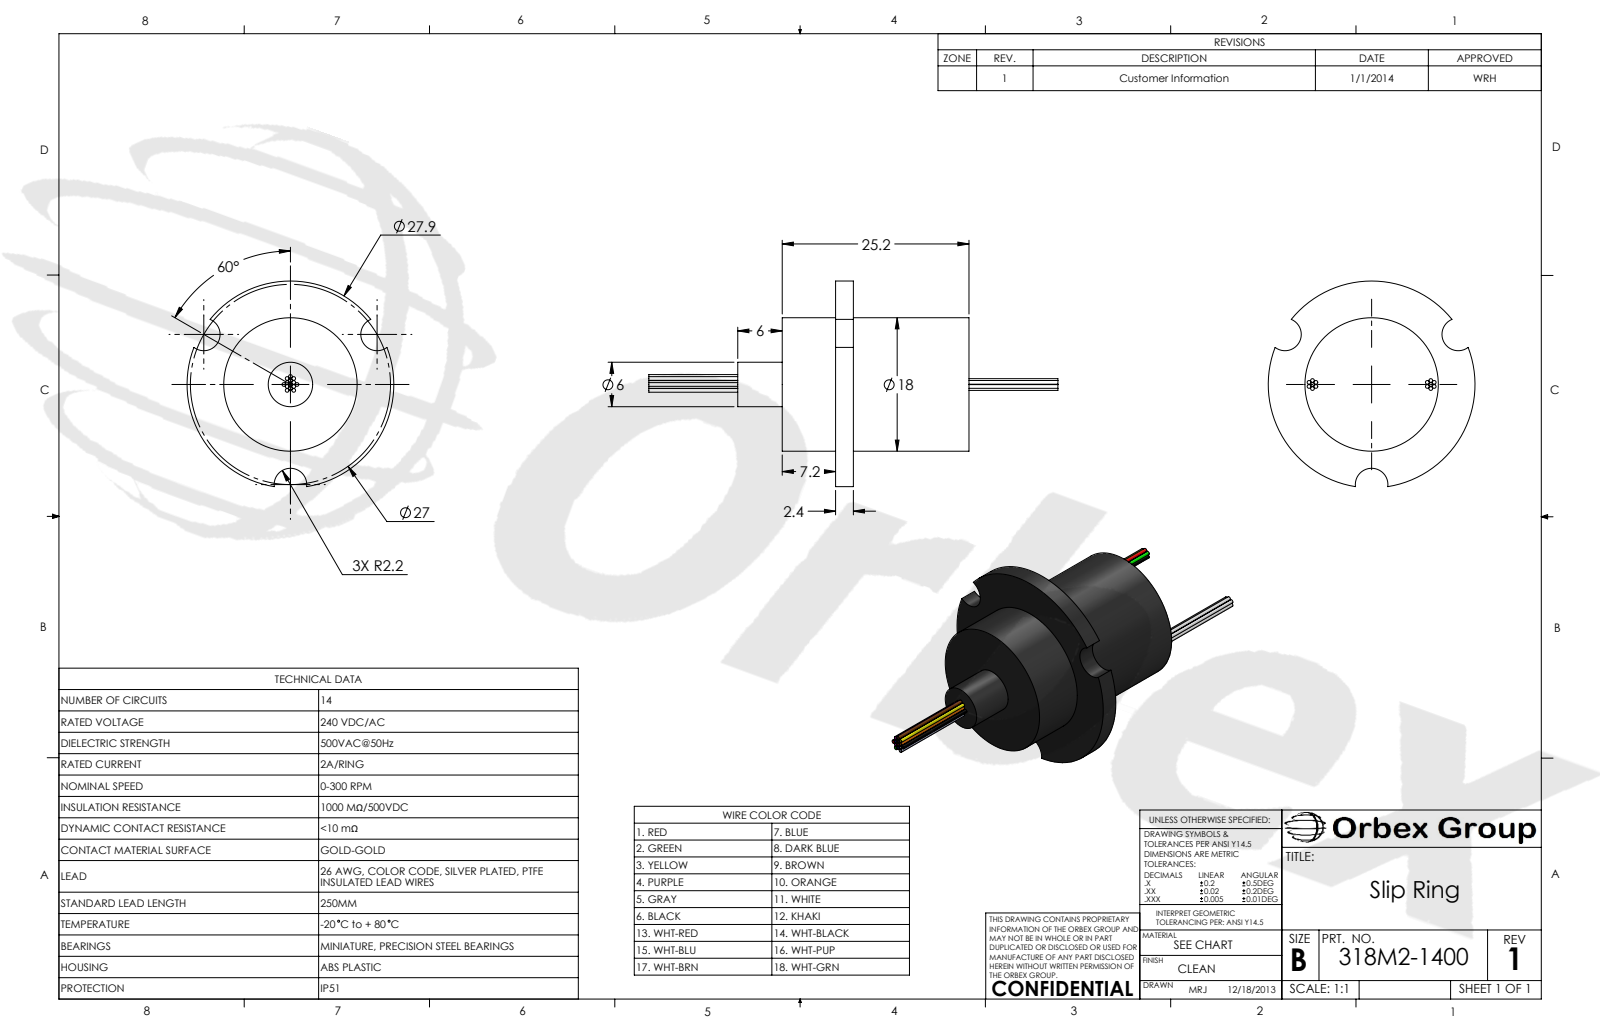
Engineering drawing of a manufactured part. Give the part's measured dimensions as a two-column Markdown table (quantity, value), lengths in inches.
| quantity | value |
| --- | --- |
| part name | 318M2-1400 Rev 1 |
| STEP written by | SolidWorks 2013 (CONFIG_CONTROL_DESIGN) |
| units | inches |
| bodies | 1 solid, 105 faces (33 planar, 72 cylindrical, 0 other) |
| overall size | 2.173 × 1.098 × 1.092 |
| volume | 0.454 in³ |
| surface area | 5.162 in² |
| round bosses / shafts (diameter × count) | 0.02 × 28, 1.098 × 1, 0.709 × 1, 0.236 × 1 |
| partial cylindrical surfaces (radius × count) | 0.087 × 3 |
| main face-to-face distances | 0.094, 0.614, 0.709, 0.992, 0.378, 0.283, 1.228, 0.52, 0.236, 0.472 |
